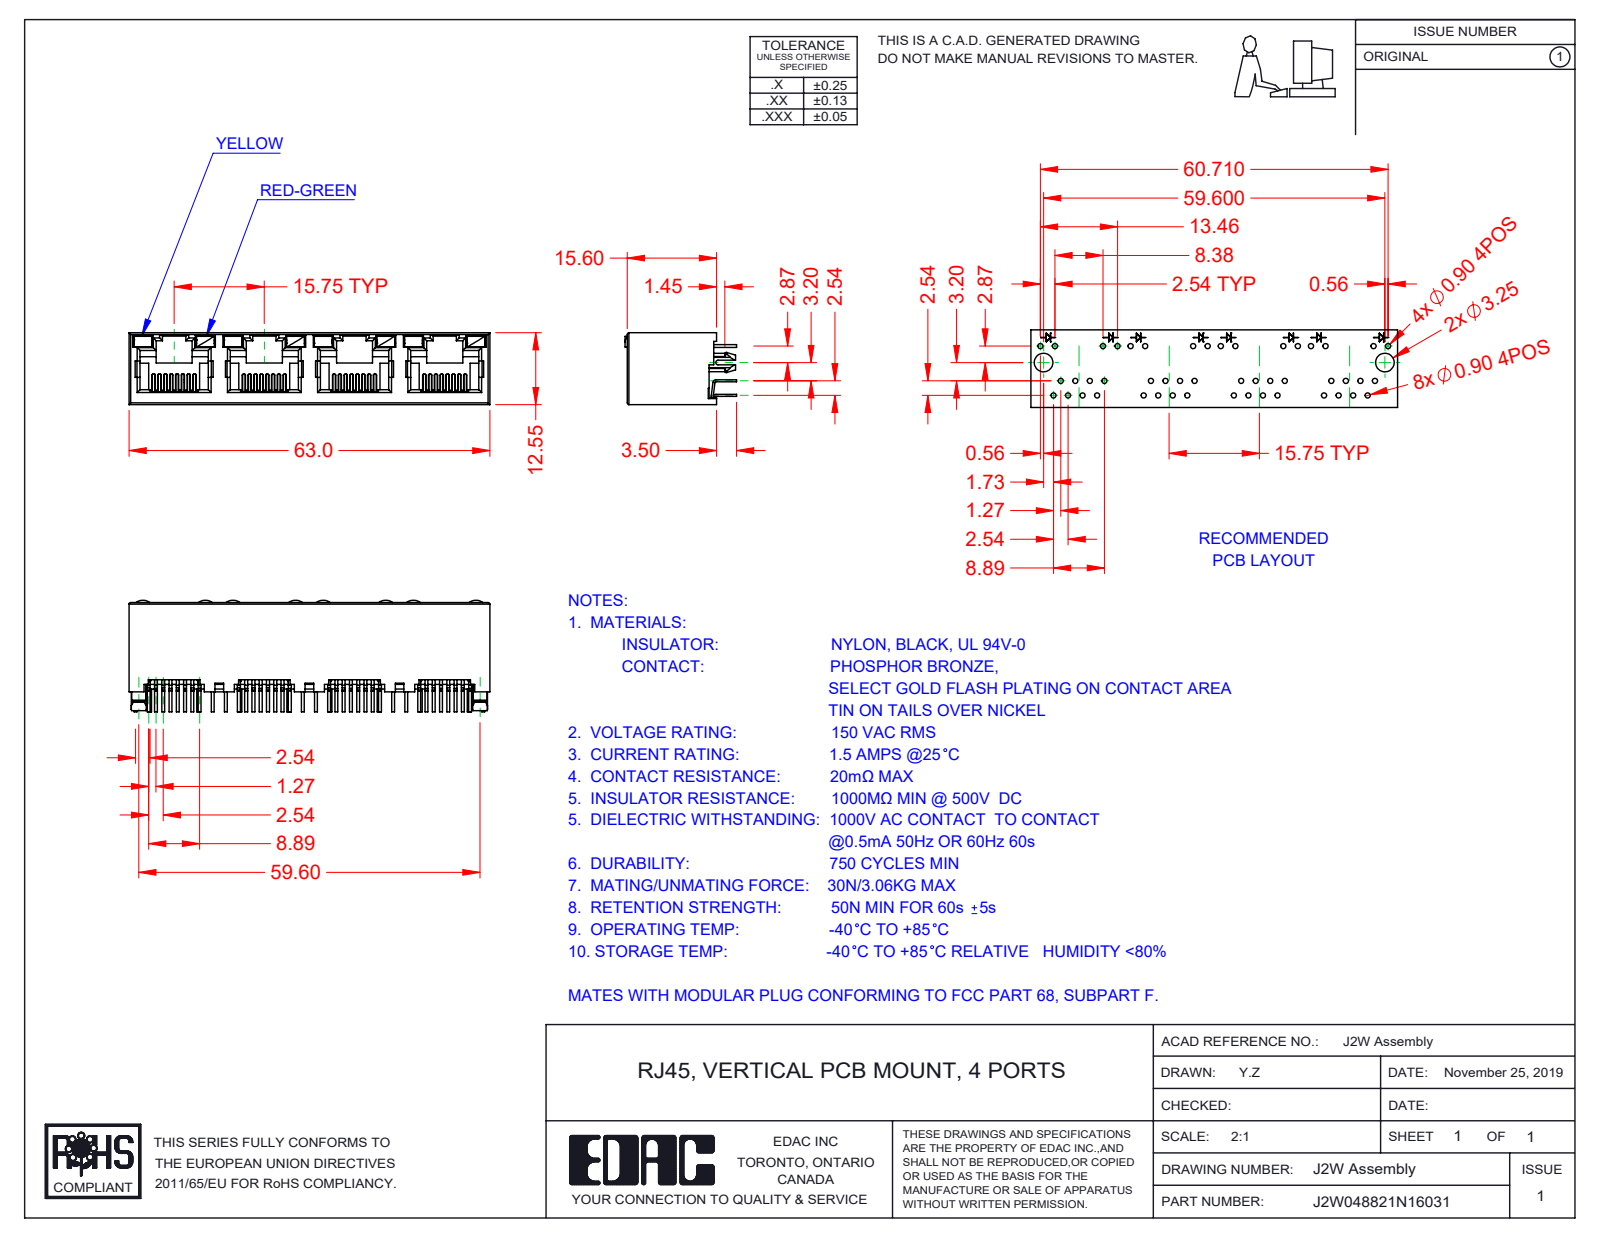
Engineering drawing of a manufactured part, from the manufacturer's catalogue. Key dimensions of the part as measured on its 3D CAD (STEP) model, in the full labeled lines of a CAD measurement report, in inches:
Part name (STEP PRODUCT): 2W LED LH_1-Yellow; J2W048821N16031; 2W Contact Lock; 2W Contacts (+2 more)
STEP written by: SolidWorks 2020 (CONFIG_CONTROL_DESIGN)
Units: inches
Bodies: 45 solids, 3139 faces (2600 planar, 481 cylindrical, 58 other)
Overall size (bounding box): 2.48 × 0.768 × 0.494
Volume: 0.326 in³ · Surface area: 20.37 in²
Partial cylindrical surfaces — rounded edges, fillets, slot ends (radius × count): R0.006 ×64, R0.008 ×29, R0.02 ×28, R0.012 ×14, R0.018 ×8, R0.079 ×8, R0.01 ×2, R0.059 ×2
Main face-to-face distances: 0.494, 0.469, 0.026, 0.62, 0.014, 0.059, 0.031, 0.024, 0.445, 1.24
